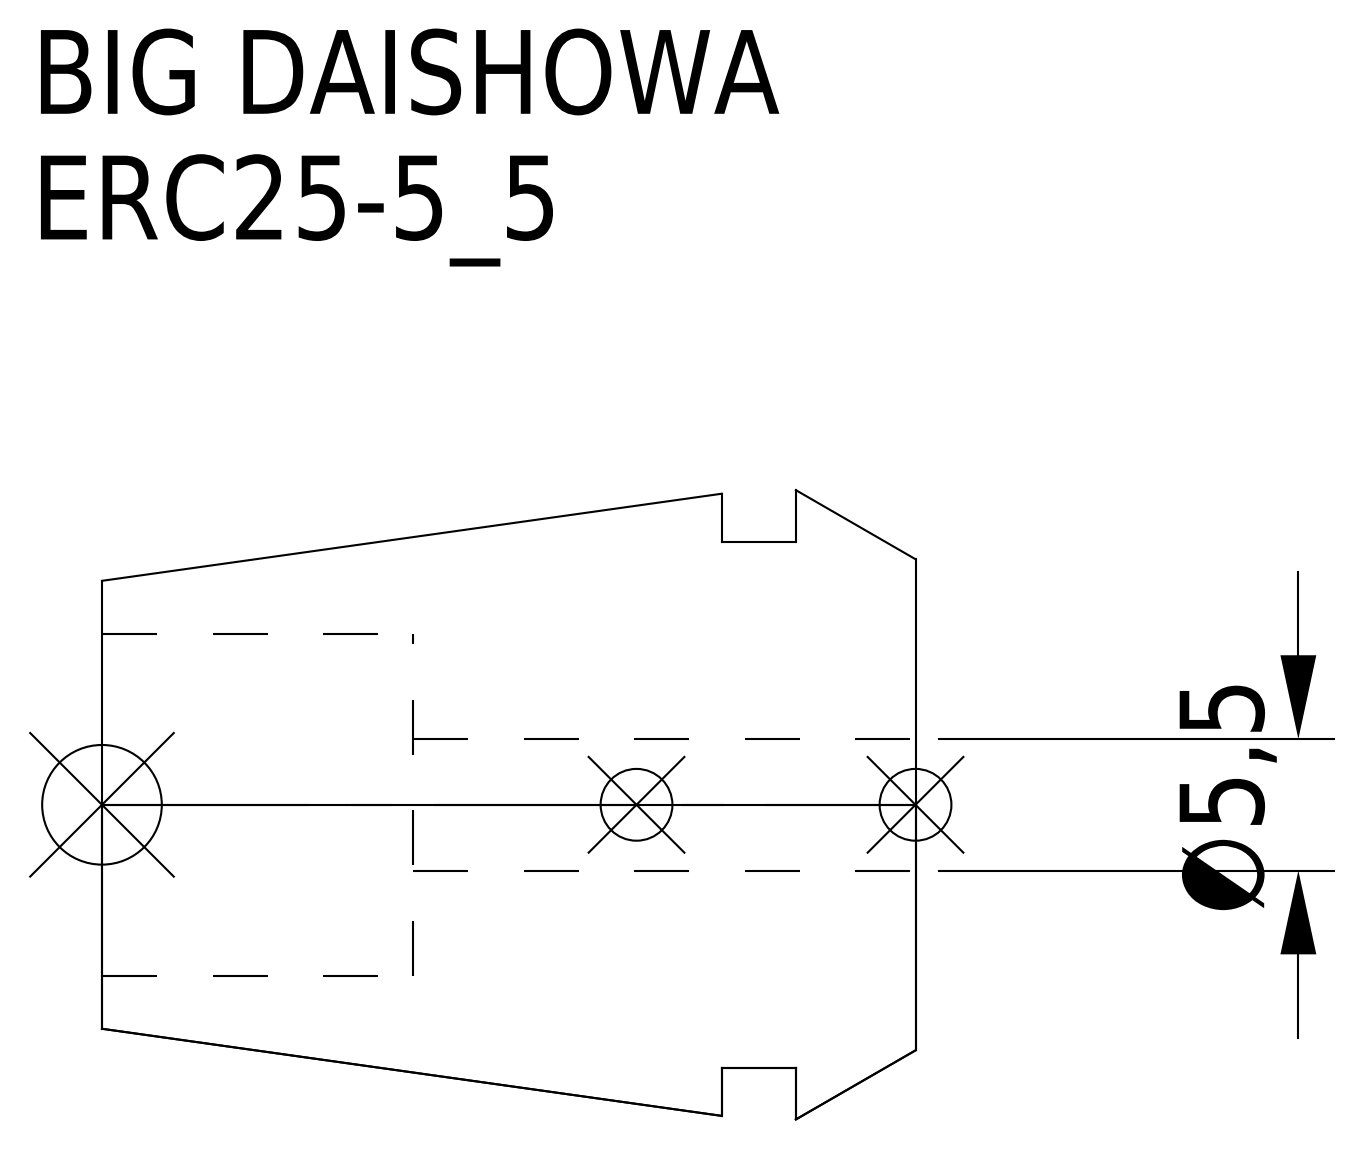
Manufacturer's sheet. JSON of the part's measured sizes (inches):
{"part_name": "ERC25-5_5", "step_written_by": "CREO PARAMETRIC BY PTC INC, 2016380 (AUTOMOTIVE_DESIGN)", "units": "inches", "bodies": {"solids": 1, "faces": 15, "planar": 5, "cylindrical": 6, "other": 4}, "overall_size": [1.339, 1.035, 1.035], "volume_in3": 0.672, "surface_area_in2": 6.659, "round_holes": [[0.217, 1], [0.563, 1]], "round_bosses_or_shafts": [[0.866, 1]], "face_to_face_distances": [0.197, 0.319, 0.122, 0.827, 0.63, 0.508, 1.339, 1.142, 1.02, 0.512]}
